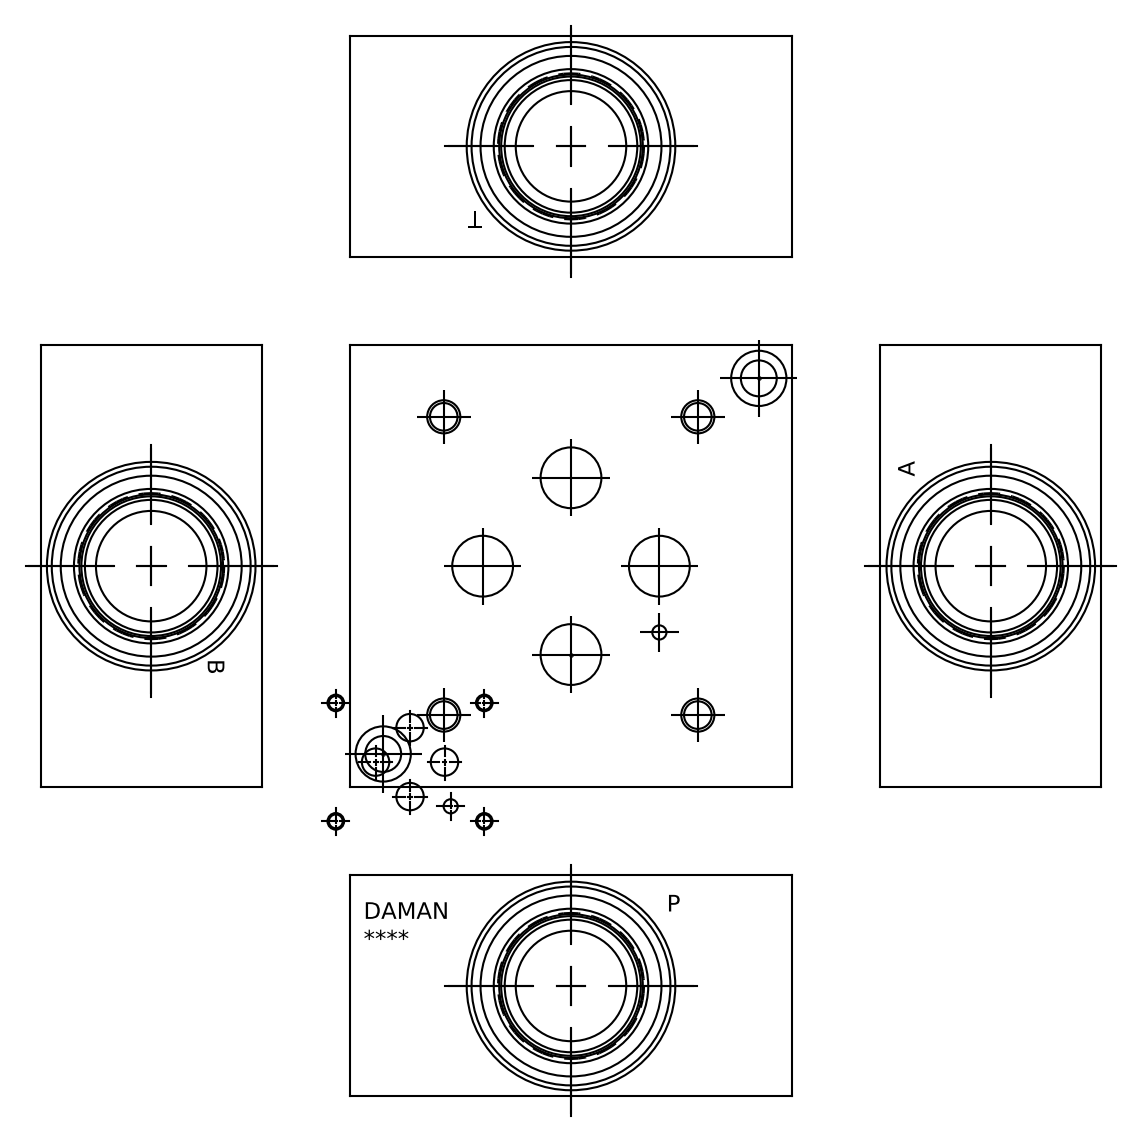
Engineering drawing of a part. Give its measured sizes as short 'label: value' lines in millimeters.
name: Part_AS06SPS20S_3D
written by: Autodesk Inventor 2020 (AUTOMOTIVE_DESIGN)
unit: mm
bodies: 1 solid, 416 faces (219 planar, 37 cylindrical, 160 other)
size: 127 × 127 × 63.5
volume: 783 285 mm³; area: 94 015 mm²
holes: 4× ⌀7.92, 4× ⌀9.53, 4× ⌀17.48, 2× ⌀10.31, 2× ⌀15.88, 2× ⌀38.1, 2× ⌀39.22, 2× ⌀41.27, 2× ⌀43.51, 2× ⌀58.57, 1× ⌀8, 1× ⌀41.28
face distances: 63.5, 127, 0.79, 126.21, 125.42, 19.84, 107.16, 19.05, 106.37, 87.32
hole spacings: 35.92, 40.44, 44.22, 75.26, 77.35, 50.8, 73, 85.6
